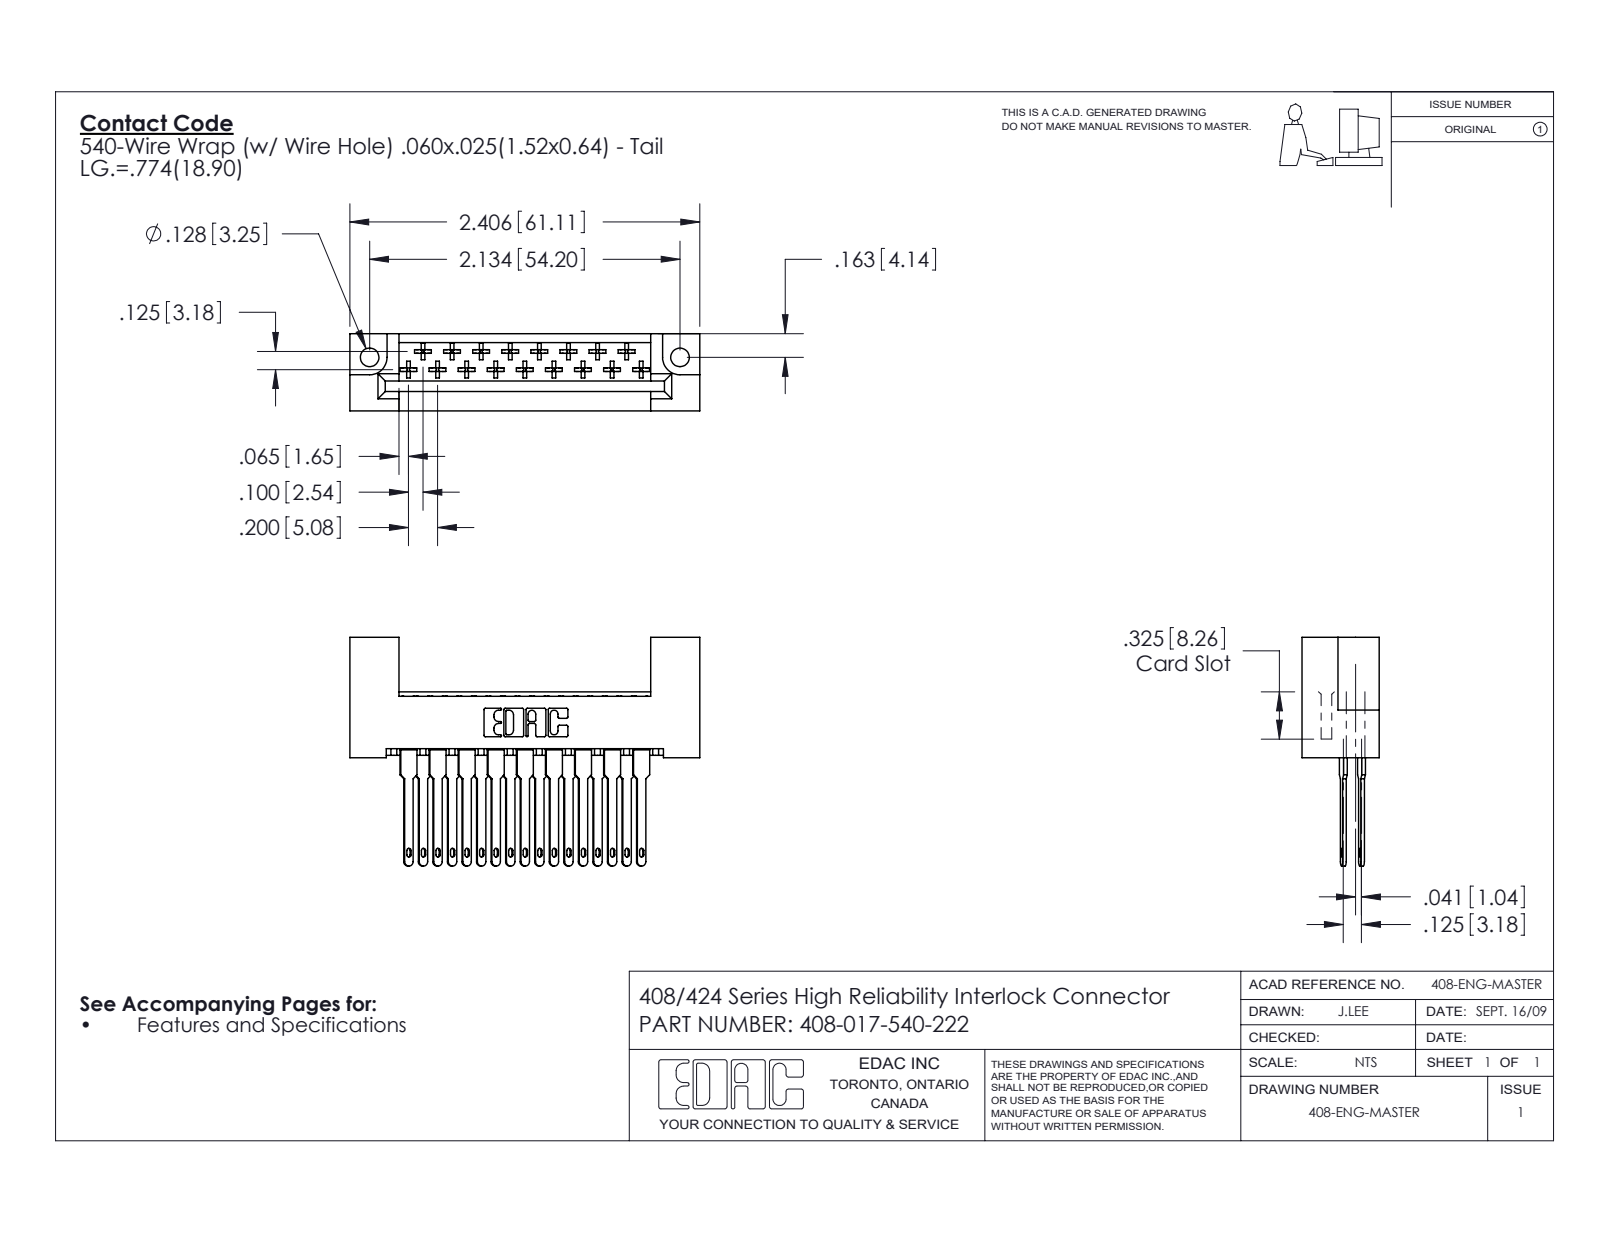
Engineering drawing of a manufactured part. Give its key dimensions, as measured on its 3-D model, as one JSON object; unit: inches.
{"part_name": "408-017-540-222; 408 Part_017 - 2; 408-290-001_408-290-140", "step_written_by": "SolidWorks 2016 (CONFIG_CONTROL_DESIGN)", "units": "inches", "bodies": {"solids": 18, "faces": 1108, "planar": 803, "cylindrical": 237, "other": 68}, "overall_size": [2.406, 1.572, 0.531], "volume_in3": 0.521, "surface_area_in2": 15.54, "round_holes": [[0.128, 2]], "partial_cylinders_radius": [[0.01, 102], [0.015, 34], [0.01, 22], [0.02, 19], [0.03, 17], [0.007, 6], [0.031, 6], [0.026, 3]], "face_to_face_distances": [0.531, 0.025, 0.125, 0.025, 0.1, 0.104, 0.095, 0.133, 0.361, 0.326], "hole_center_spacings": [2.134]}
